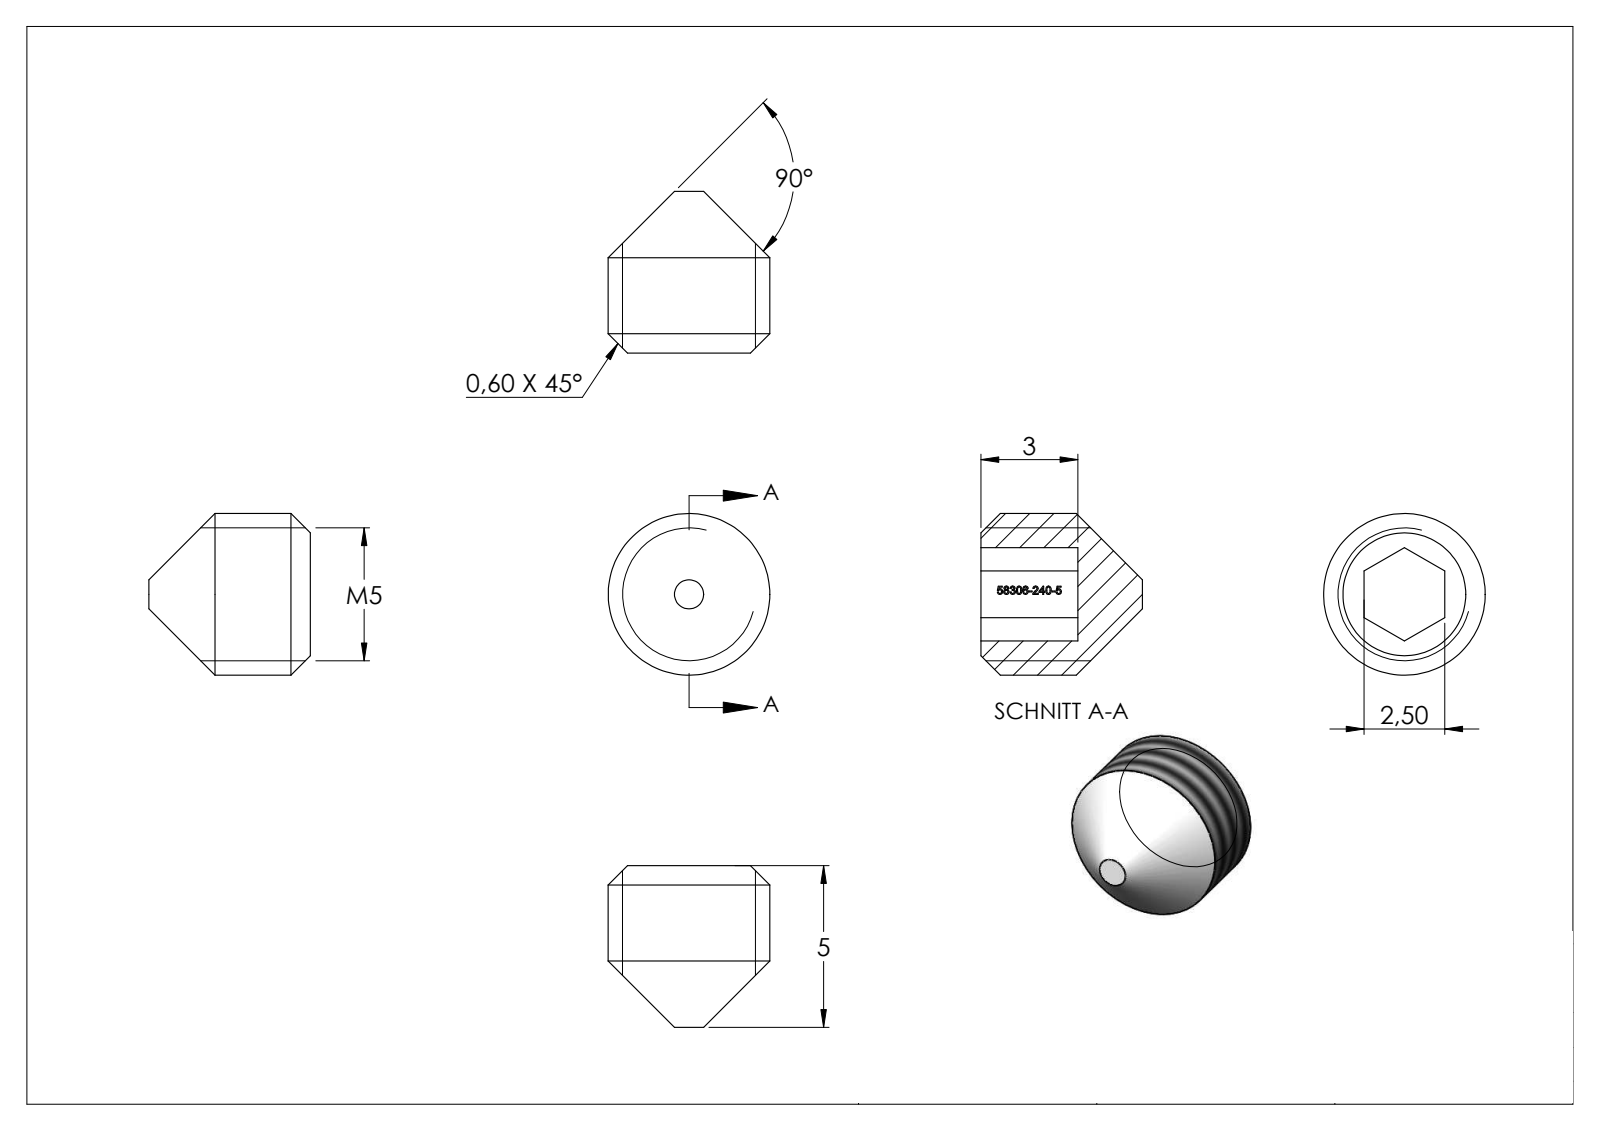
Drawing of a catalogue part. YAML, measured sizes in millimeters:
part_name: "58306-240-5"
step_written_by: "SolidWorks 2015 (CONFIG_CONTROL_DESIGN)"
units: millimeters
bodies: {solids: 1, faces: 165, planar: 70, cylindrical: 1, other: 94}
overall_size: [70, 5, 5]
volume: 55
surface_area: 115
round_bosses_or_shafts:
  - {diameter: 5, count: 1}
face_to_face_distances: [2.5, 3, 2, 5, 2.6, 3.06, 1.06, 1.94, 3.09, 1.09]
